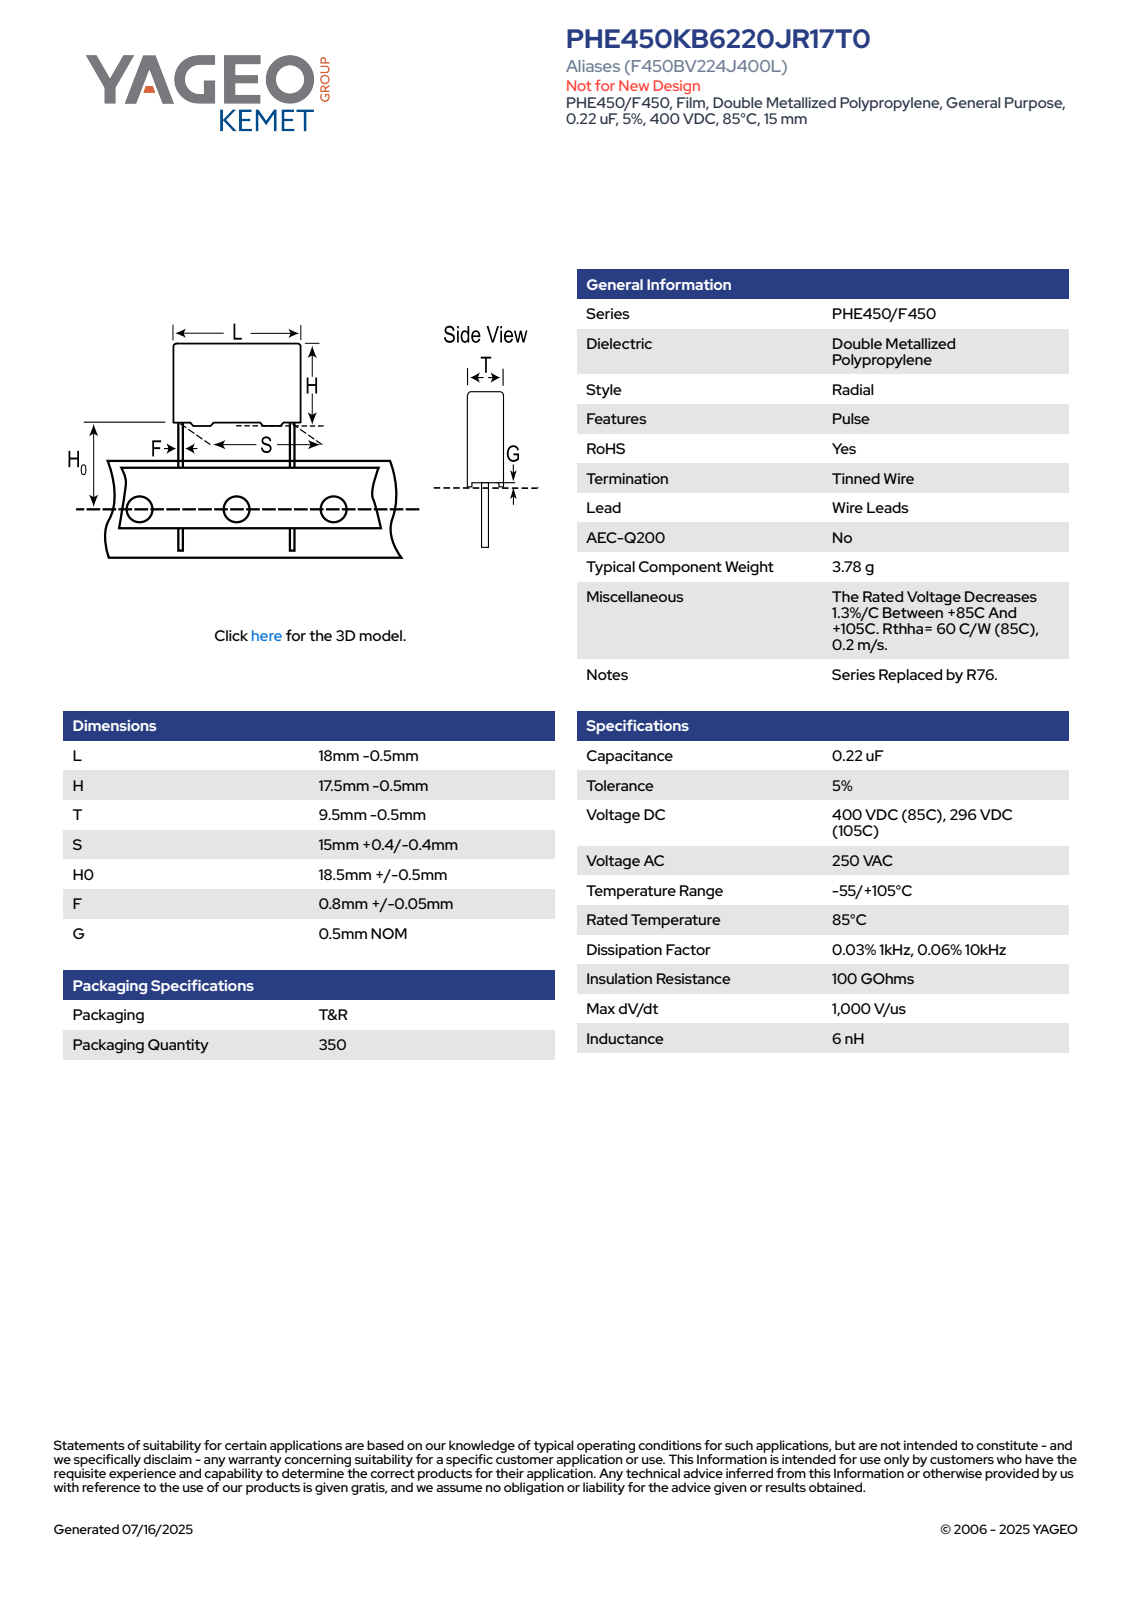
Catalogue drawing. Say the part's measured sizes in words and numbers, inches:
The part is named "CFR_RBG_18X17.5X9.5_L17.5H17T9S15H019F0.85G0.5". Its 3-D file was written by "SolidWorks 2014 (AUTOMOTIVE_DESIGN)". It is 4 solids with 89 faces: 81 planar, 8 cylindrical and 0 other. Overall it measures 1.417 by 0.689 by 0.355 inches. Its volume is 0.16 cubic inches and its surface area 2.058 square inches. Round bosses or shafts: 2 of diameter 0.033. Partial cylindrical surfaces (rounded edges, fillets, slot ends): 4 of radius 0.02. The main face-to-face distances are 0.354, 0.689, 0.65, 0.02, 0.334, 0.02, 0.669, 0.314, 0.748, 0.768.
